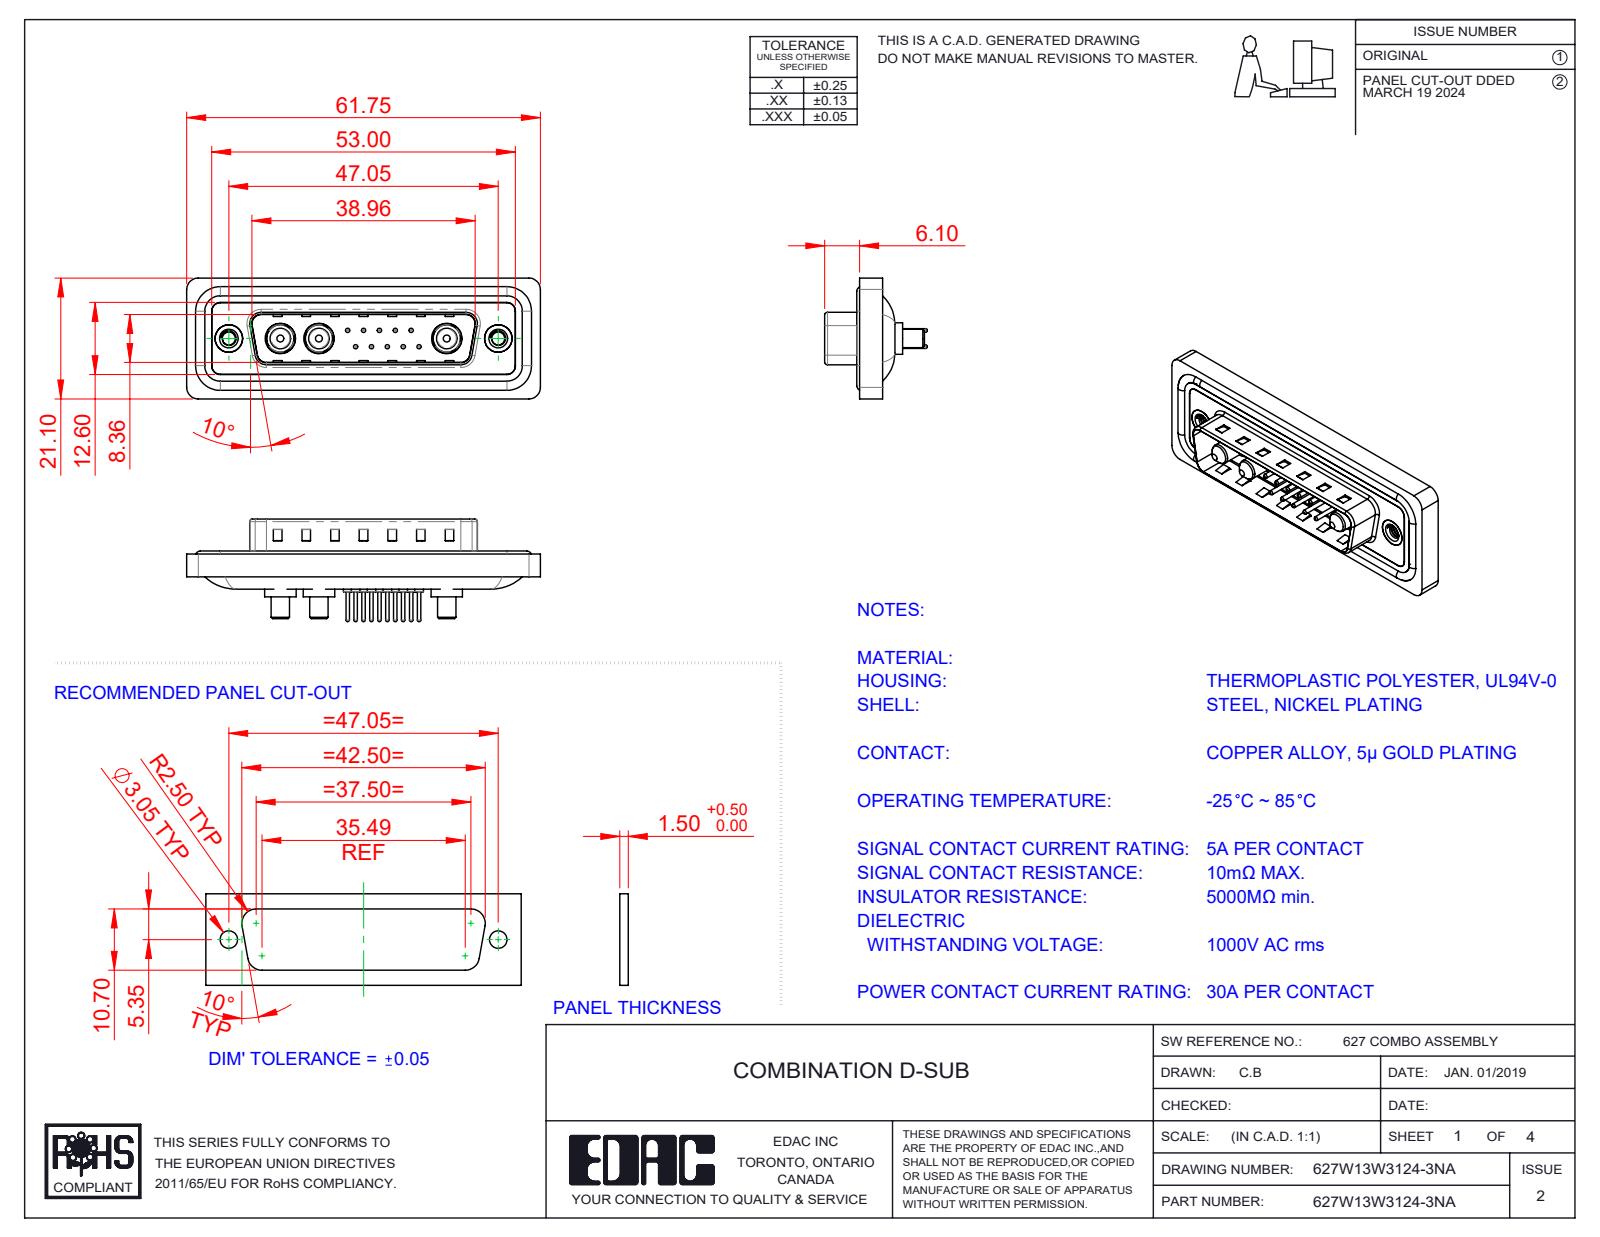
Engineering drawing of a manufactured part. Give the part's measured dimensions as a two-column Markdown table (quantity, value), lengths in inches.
| quantity | value |
| --- | --- |
| part name | 627Combo Contact Row 1_24; 627Combo Housing_13W3; 627Combo Shell Front_25 Contacts; 627Combo Shell Rear_25 Contacts (+5 more) |
| STEP written by | SolidWorks 2023 (CONFIG_CONTROL_DESIGN) |
| units | inches |
| bodies | 23 solids, 968 faces (309 planar, 387 cylindrical, 272 other) |
| overall size | 2.431 × 0.831 × 0.705 |
| volume | 0.449 in³ |
| surface area | 18.42 in² |
| round holes (diameter × count) | 0.03 × 10, 0.063 × 10, 0.079 × 10, 0.191 × 3, 0.209 × 3, 0.089 × 2, 0.157 × 2, 0.189 × 2, 0.197 × 2 |
| round bosses / shafts (diameter × count) | 0.059 × 10, 0.024 × 10, 0.063 × 4, 0.217 × 3, 0.205 × 3, 0.187 × 3, 0.148 × 3, 0.142 × 3 |
| partial cylindrical surfaces (radius × count) | 0.059 × 22, 0.079 × 18, 0.02 × 8, 0.063 × 8, 0.01 × 4, 0.024 × 4, 0.026 × 4, 0.035 × 4 |
| main face-to-face distances | 0.016, 0.059, 0.043, 0.063, 0.02, 0.122, 0.114, 0.032, 0.377, 0.161 |
| hole center spacings | 0.124, 0.109, 0.198, 0.218, 0.295, 0.198, 0.327, 0.398 |
